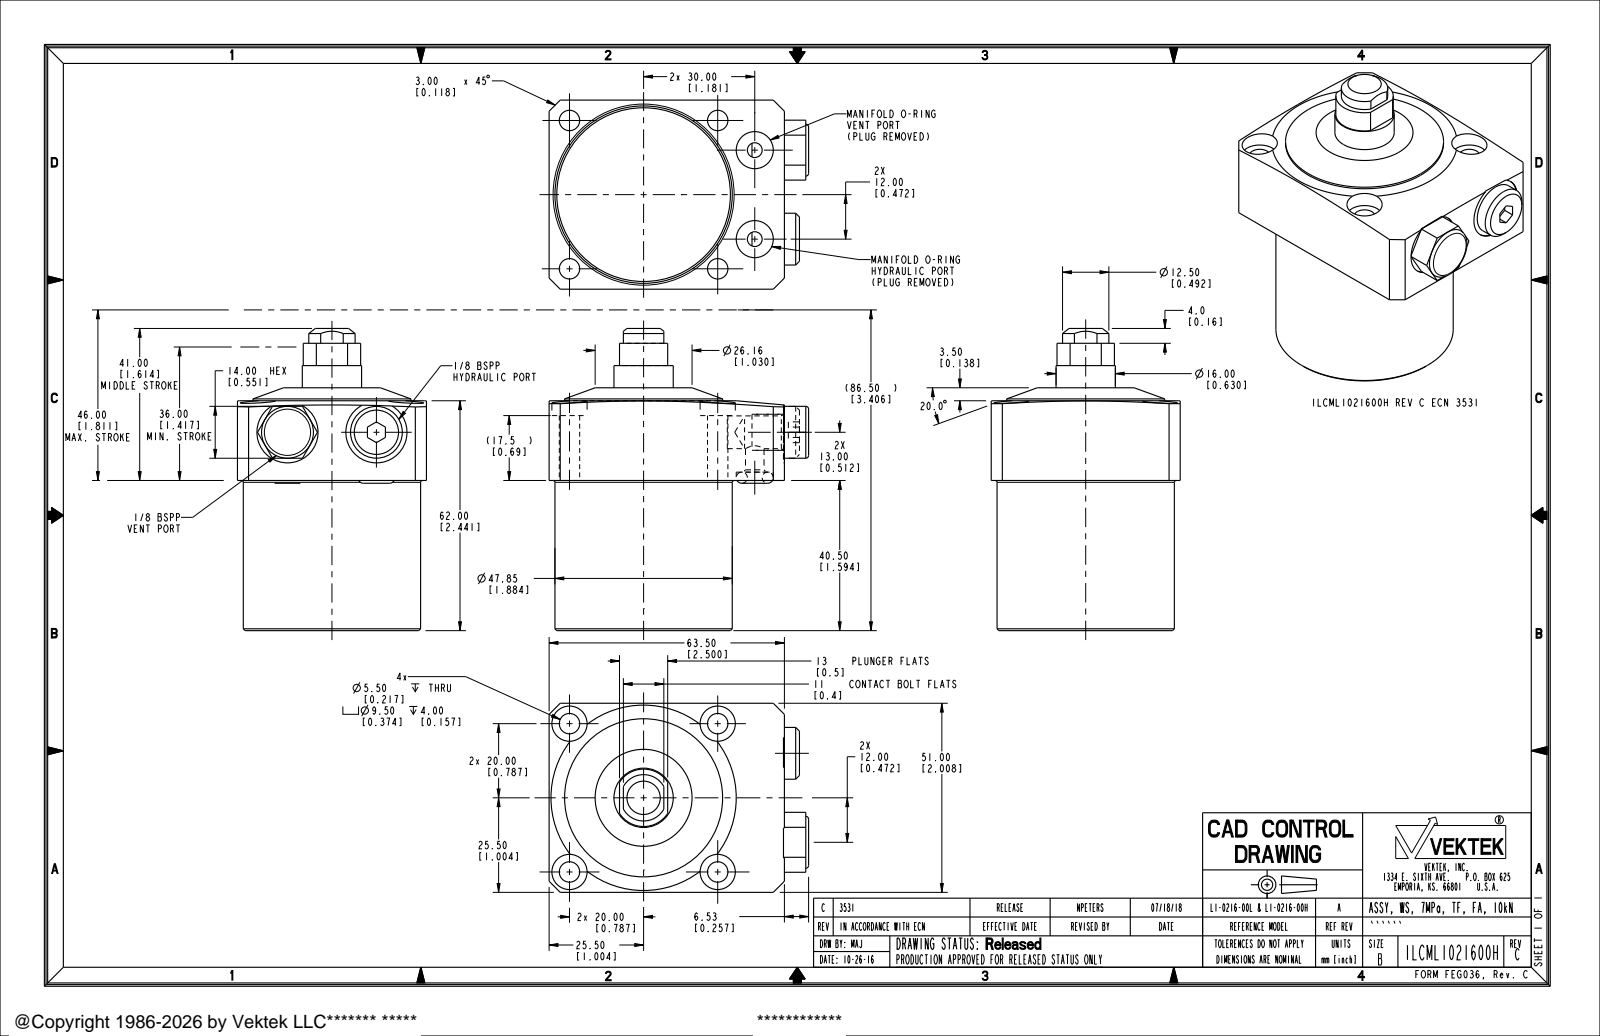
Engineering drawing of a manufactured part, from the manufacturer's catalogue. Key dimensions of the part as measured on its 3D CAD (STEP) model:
Part name (STEP PRODUCT): ILCML1021600H
STEP written by: PRO/ENGINEER BY PARAMETRIC TECHNOLOGY CORPORATION, 2013320 (AUTOMOTIVE_DESIGN)
Units: millimetres
Bodies: 4 solids, 137 faces (55 planar, 50 cylindrical, 32 other)
Overall size (bounding box): 81.5 × 70.03 × 51
Volume: 144 208 mm³ · Surface area: 22 532 mm²
Round holes (diameter × count): ⌀5.5 ×4, ⌀9.5 ×4, ⌀5 ×2, ⌀6 ×2, ⌀8.84 ×2, ⌀10 ×2, ⌀16.5 ×2
Round bosses / shafts (diameter × count): ⌀47.85 ×1, ⌀42.64 ×1, ⌀16 ×1, ⌀13.97 ×1, ⌀9.73 ×1, ⌀9.72 ×1
Partial cylindrical surfaces — rounded edges, fillets, slot ends (radius × count): R6.25 ×1, R7.75 ×1
Main face-to-face distances: 51, 40.5, 63.5, 62, 21.5, 65.5, 25, 3.5, 63.25, 4
Hole centre spacings: 40, 12.81, 24, 33.53, 50.64, 56.57, 59.36
